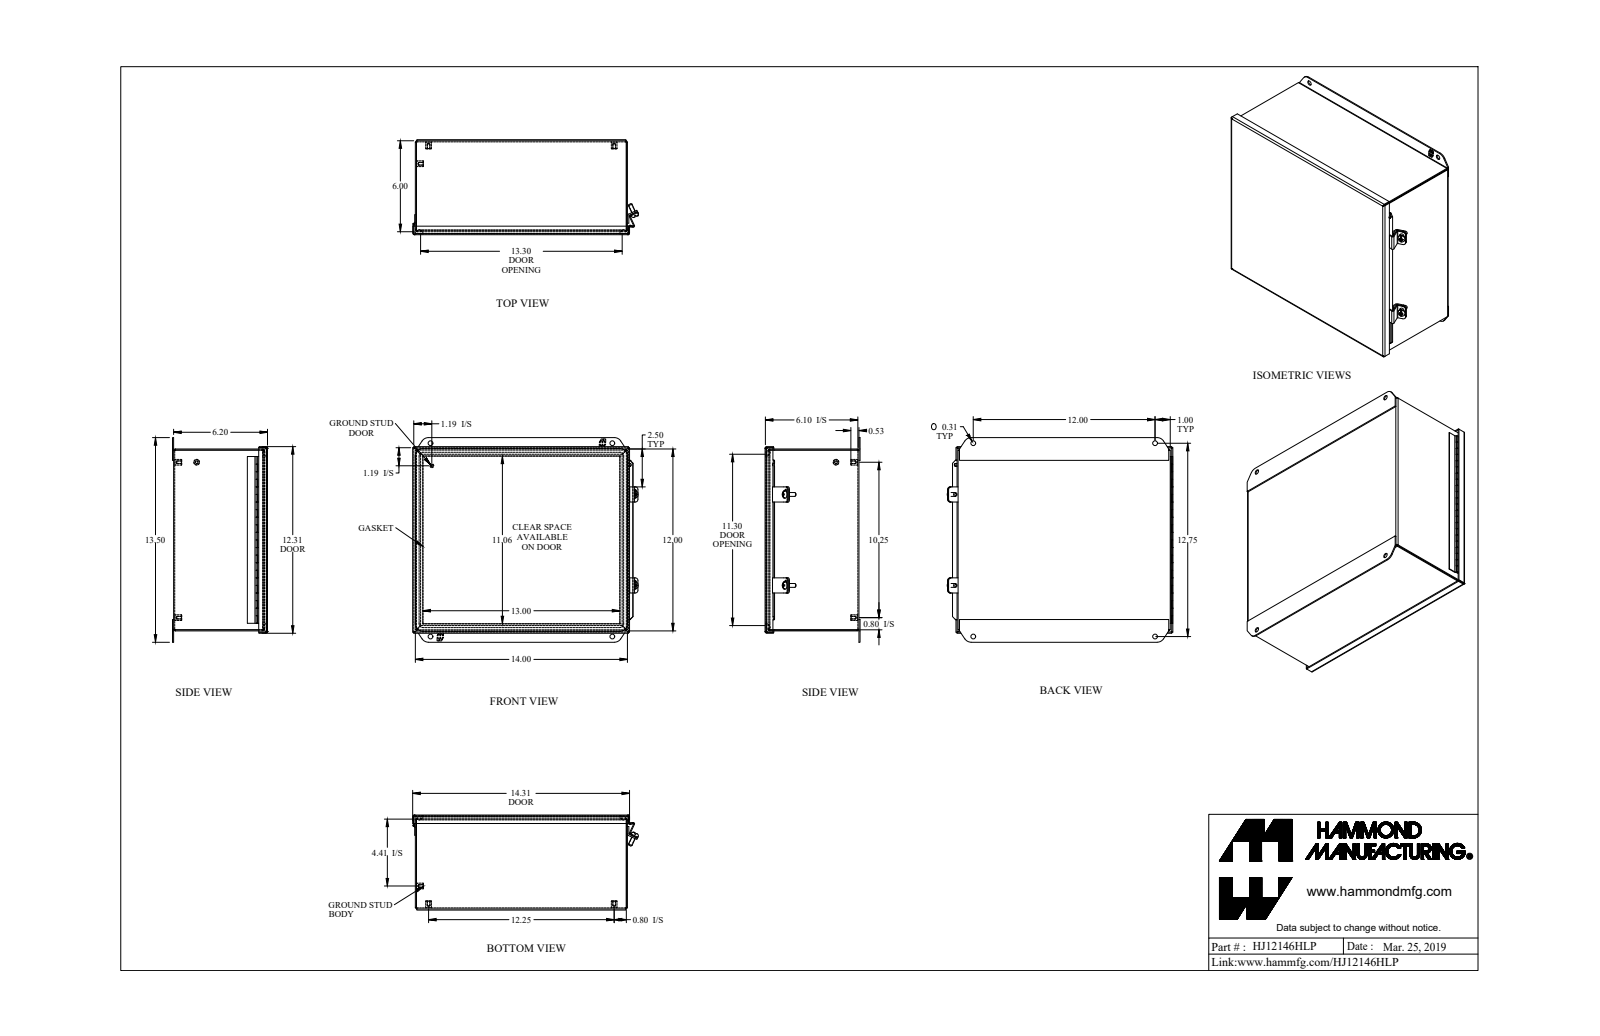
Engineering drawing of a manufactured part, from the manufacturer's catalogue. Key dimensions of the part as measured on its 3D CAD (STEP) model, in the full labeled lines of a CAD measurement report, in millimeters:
Part name (STEP PRODUCT): HJ12146HLP
STEP written by: SolidWorks 2018 (AUTOMOTIVE_DESIGN)
Units: millimetres
Bodies: 20 solids, 773 faces (414 planar, 231 cylindrical, 128 other)
Overall size (bounding box): 378.4 × 342.9 × 159.2
Volume: 958 200 mm³ · Surface area: 1 057 000 mm²
Round holes (diameter × count): ⌀4 ×5, ⌀8 ×4, ⌀5.4 ×2, ⌀1.3 ×1
Round bosses / shafts (diameter × count): ⌀9.5 ×5, ⌀6.4 ×3, ⌀12.2 ×2, ⌀4.8 ×1, ⌀2.5 ×1, ⌀1.1 ×1
Partial cylindrical surfaces — rounded edges, fillets, slot ends (radius × count): R6.4 ×16, R0.9 ×13, R2.7 ×13, R0.3 ×4, R3.6 ×4, R4.8 ×4, R12.7 ×4, R12.7 ×4
Main face-to-face distances: 1.8, 155.6, 157.4, 153.7, 303, 353.8, 304.8, 301.1, 351.9, 355.6
Hole centre spacings: 31.9, 292.1, 309.6, 424.5, 260.4, 304.8, 311.2, 323.9
